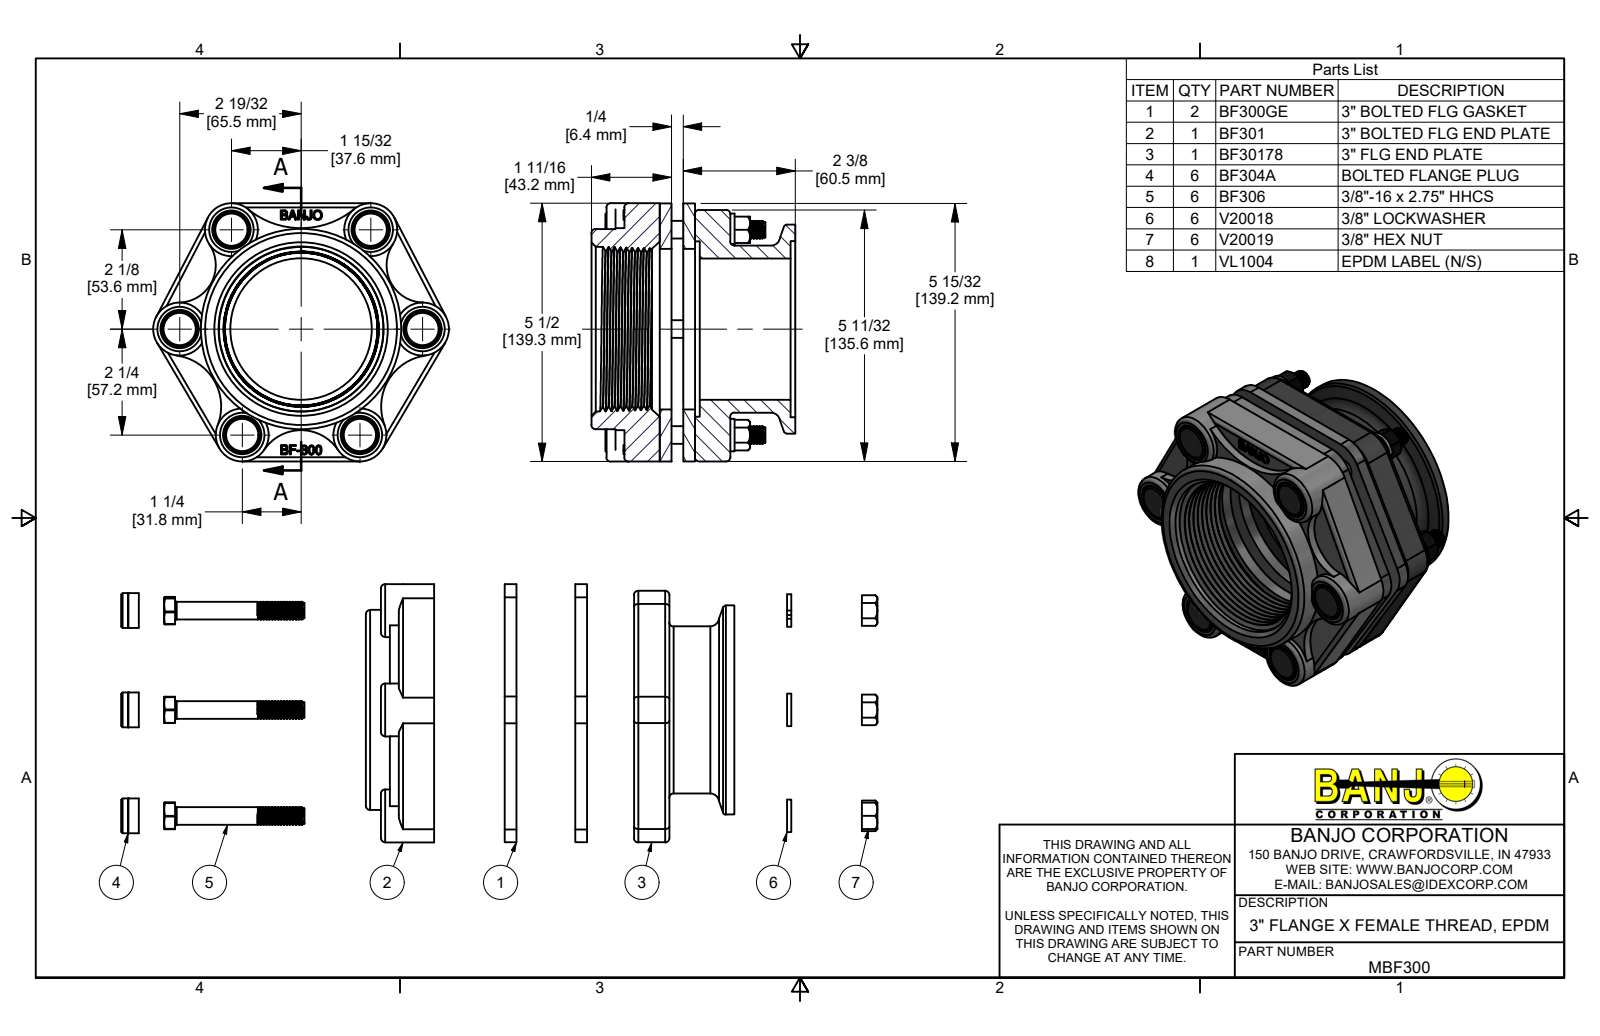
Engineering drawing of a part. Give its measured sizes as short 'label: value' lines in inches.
name: MBF300; BF301; BF30178; BF304A (+4 more)
written by: Autodesk Inventor 2019 (AUTOMOTIVE_DESIGN)
unit: in
bodies: 28 solids, 1480 faces (454 planar, 470 cylindrical, 556 other)
size: 6.285 × 5.485 × 4.33
volume: 46.89 in³; area: 330.6 in²
holes: 6× ⌀0.307, 6× ⌀0.385, 6× ⌀0.406, 6× ⌀0.41, 6× ⌀0.715, 6× ⌀0.75, 1× ⌀3, 1× ⌀3.41, 1× ⌀3.725, 1× ⌀3.74
bosses: 90× ⌀0.324, 6× ⌀1.125, 6× ⌀0.742, 6× ⌀0.687, 6× ⌀0.375, 1× ⌀4.44, 1× ⌀4.25, 1× ⌀3.55
rounds: 18× R0.09, 12× R0.162, 12× R0.562, 6× R0.32, 2× R0.794, 2× R1.094, 1× R0.942, 1× R1.777
face distances: 0.25, 0.75, 0.5, 1.25, 1, 1.5, 0.1, 2.03, 1.38, 2.13
hole spacings: 2.38, 2.574, 2.577, 2.614, 4.366, 4.442, 4.576, 5.144
